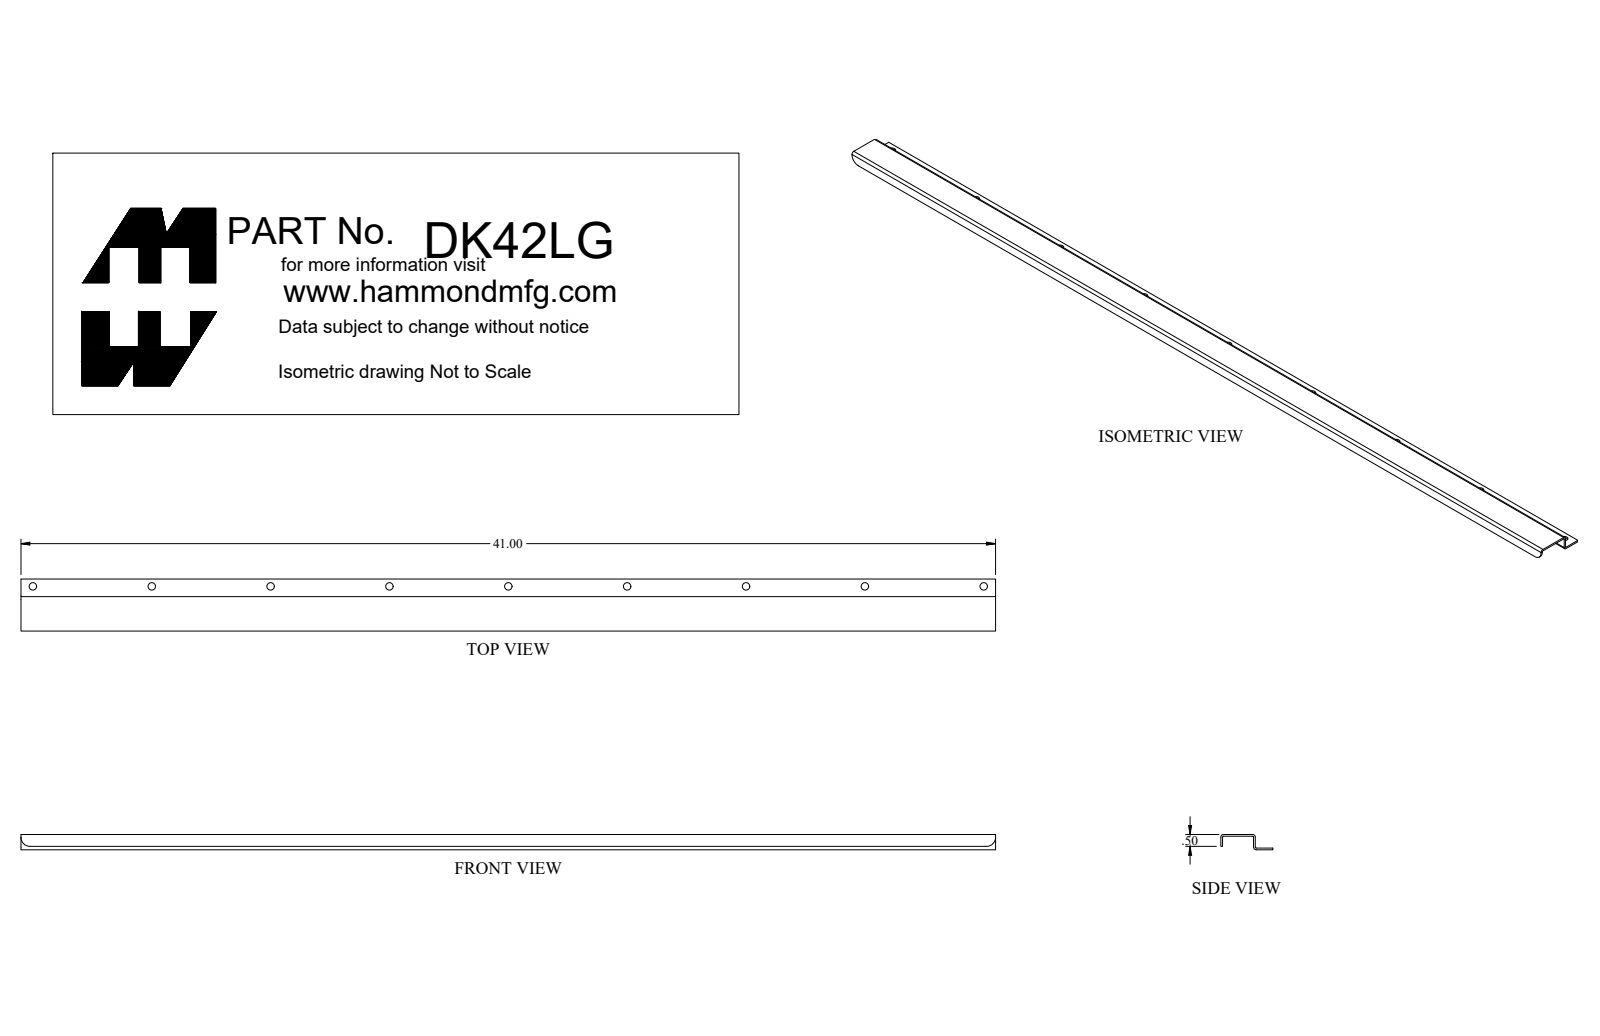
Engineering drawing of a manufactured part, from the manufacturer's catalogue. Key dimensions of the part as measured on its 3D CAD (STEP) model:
Part name (STEP PRODUCT): DK42LG_Default
STEP written by: SolidWorks 2018 (CONFIG_CONTROL_DESIGN)
Units: inches
Bodies: 5 solids, 77 faces (35 planar, 36 cylindrical, 6 other)
Overall size (bounding box): 41 × 2.188 × 1.322
Volume: 11.13 in³ · Surface area: 328.7 in²
Round holes (diameter × count): ⌀0.313 ×9, ⌀0.201 ×1, ⌀0.275 ×1
Round bosses / shafts (diameter × count): ⌀0.625 ×1, ⌀0.483 ×1, ⌀0.25 ×1
Partial cylindrical surfaces — rounded edges, fillets, slot ends (radius × count): R0.036 ×3, R0.108 ×3, R0.375 ×2
Main face-to-face distances: 0.072, 0.572, 0.644, 1.376, 0.5, 0.063, 0.635, 0.707, 0.135, 1.448
Hole centre spacings: 5, 10, 15, 20, 25, 30, 35, 40
